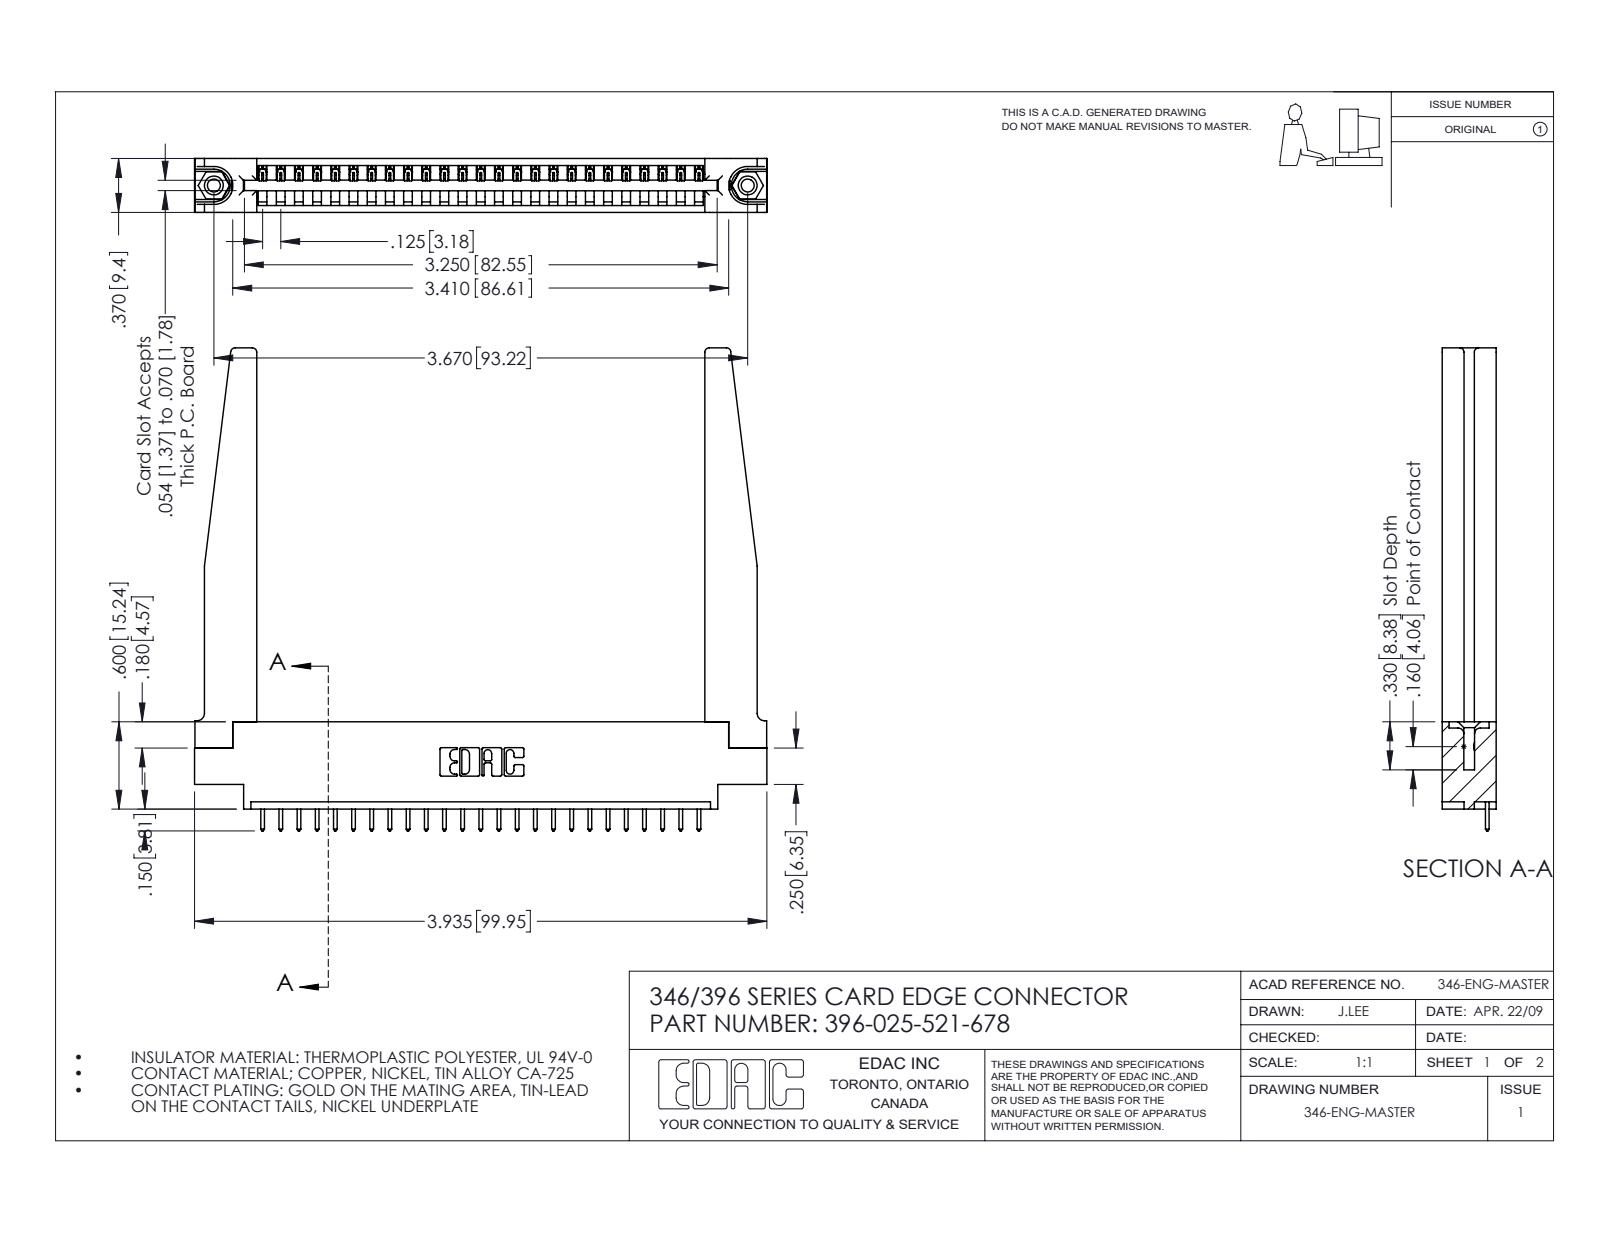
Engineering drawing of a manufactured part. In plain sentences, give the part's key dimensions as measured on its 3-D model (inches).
The part is named "346 Part_0.170 Offset - 0.156 Dia-TH; 345-292-001_345-293-121; 396-025-521-678; 345-250-001_345-250-001-102 (+1 more)". Its 3-D file was written by "SolidWorks 2016 (CONFIG_CONTROL_DESIGN)". It is 30 solids with 1810 faces: 1222 planar, 536 cylindrical and 52 other. Overall it measures 3.935 by 3.32 by 0.37 inches. Its volume is 0.985 cubic inches and its surface area 27.53 square inches. Round holes: 2 of diameter 0.089, 2 of diameter 0.125, 2 of diameter 0.156, 1 of diameter 0.064. Round bosses or shafts: 2 of diameter 0.155. Partial cylindrical surfaces (rounded edges, fillets, slot ends): 50 of radius 0.006, 50 of radius 0.01, 22 of radius 0.01, 8 of radius 0.03, 6 of radius 0.007, 6 of radius 0.031, 3 of radius 0.026, 2 of radius 0.031. The main face-to-face distances are 0.37, 0.048, 0.322, 0.072, 0.148, 0.15, 0.25, 0.298, 0.025, 0.222. The hole center spacings are 0.246, 3.462, 3.67.
